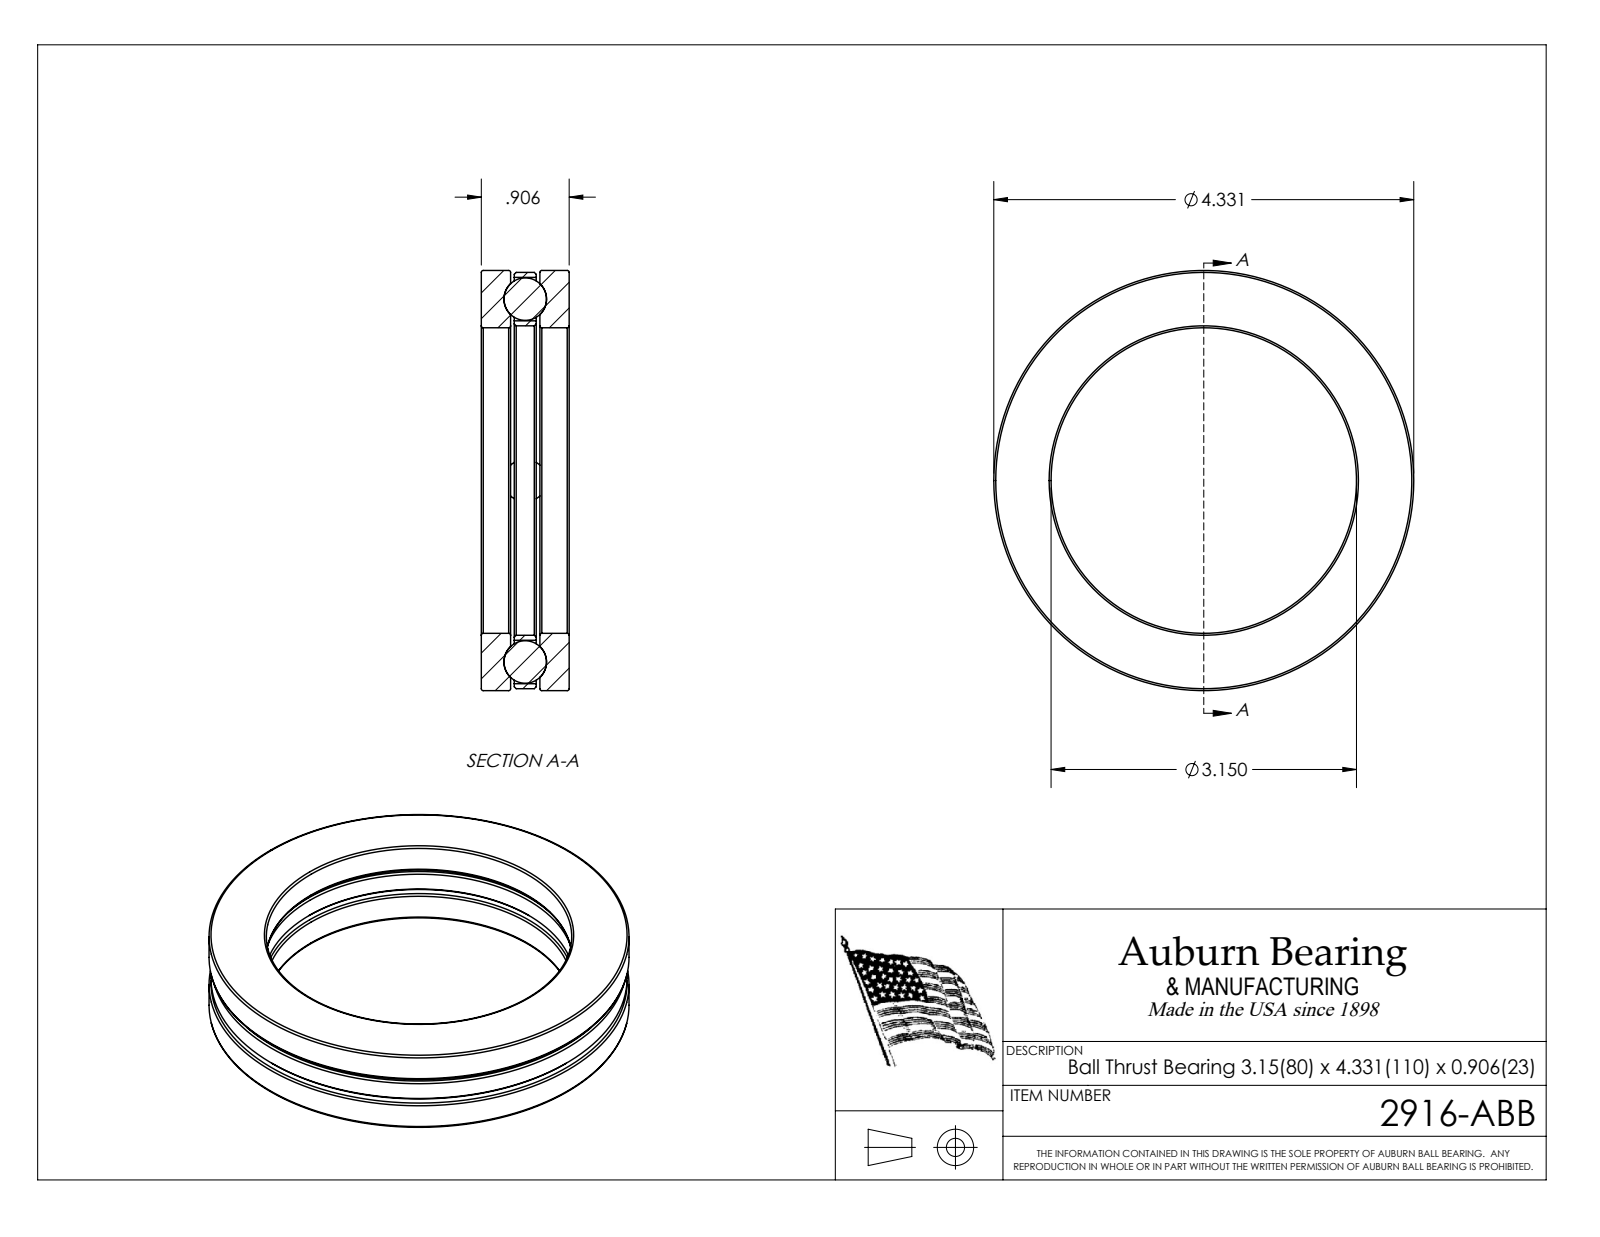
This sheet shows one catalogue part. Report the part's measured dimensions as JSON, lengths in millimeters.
{"part_name": "2916-ABB", "step_written_by": "SolidWorks 2017 (CONFIG_CONTROL_DESIGN)", "units": "millimeters", "bodies": {"solids": 7, "faces": 36, "planar": 8, "cylindrical": 10, "other": 18}, "overall_size": [110, 110, 23], "volume_mm3": 87210, "surface_area_mm2": 40100, "round_holes": [[11.4, 4], [80, 1], [81, 1]], "round_bosses_or_shafts": [[110, 1], [109, 1]], "face_to_face_distances": [8.6, 14.4, 23, 7.7, 15.3, 1, 6.7, 5.8, 7.7], "hole_center_spacings": [47.5, 67.2, 95]}
